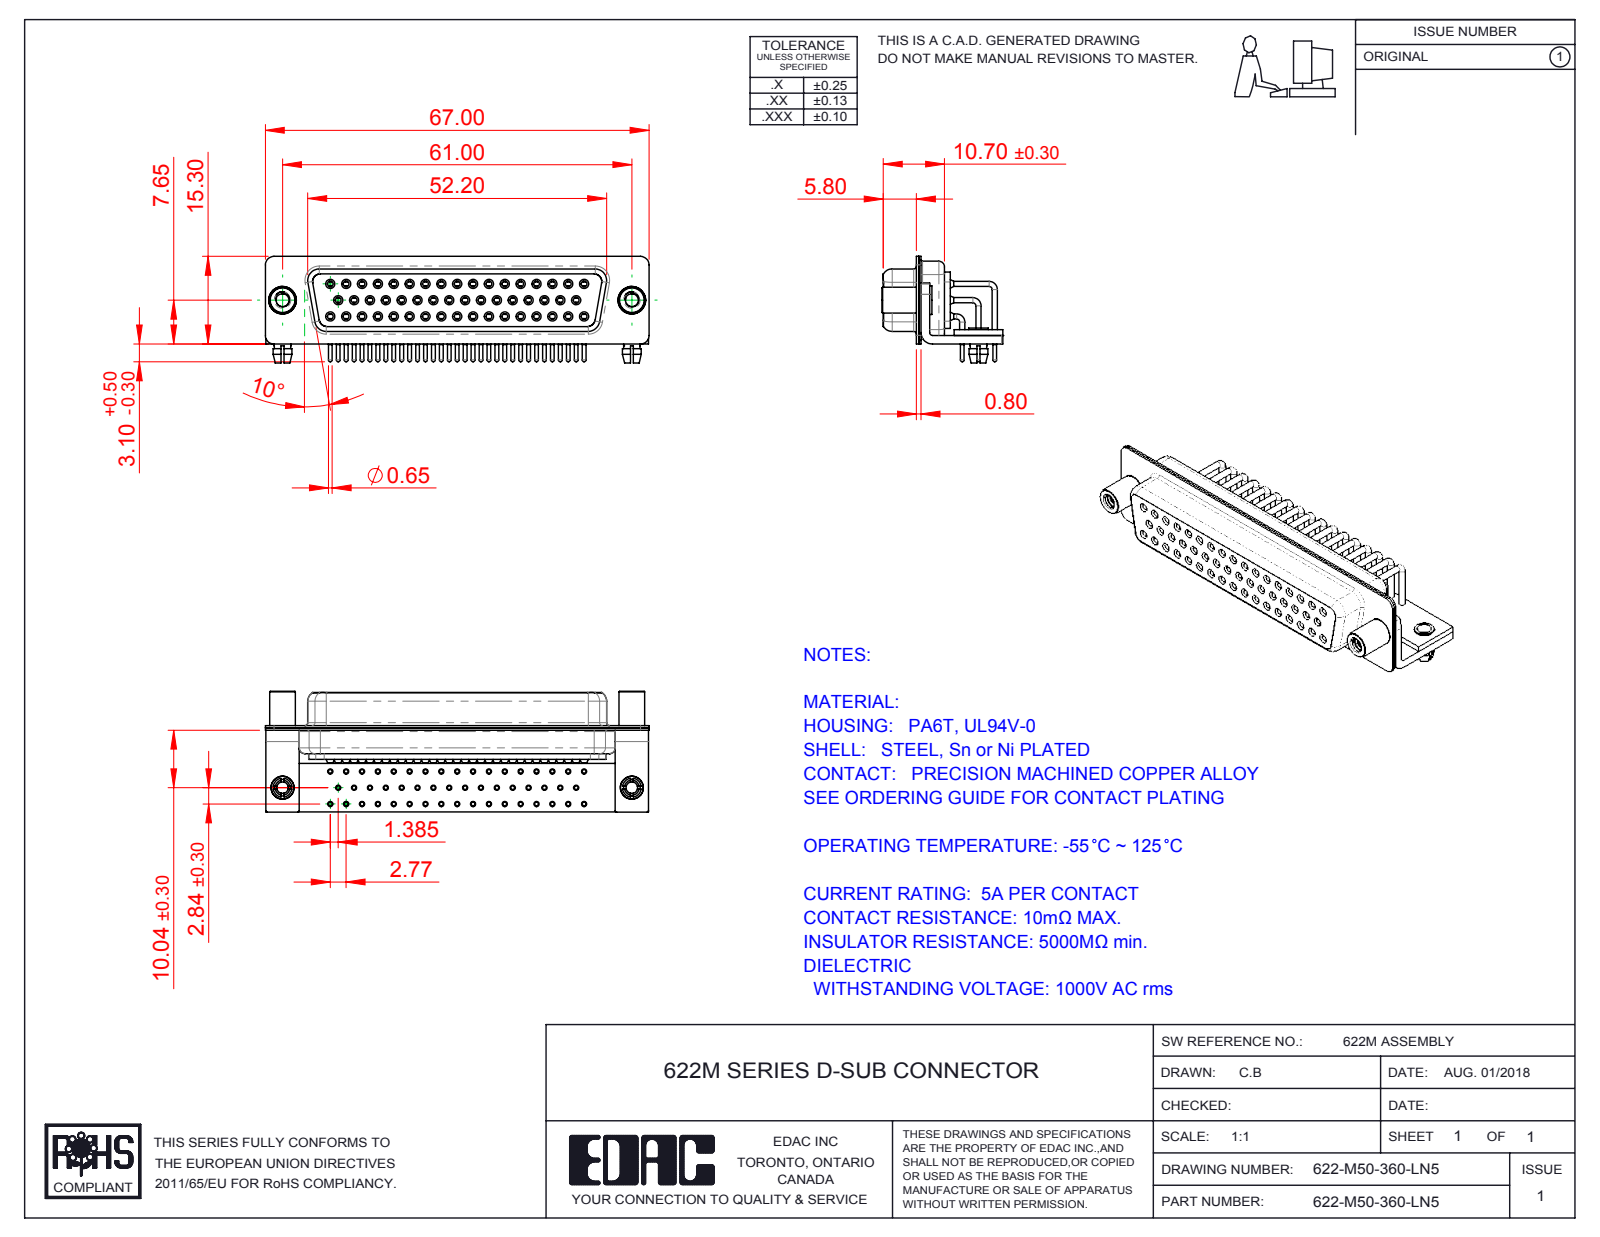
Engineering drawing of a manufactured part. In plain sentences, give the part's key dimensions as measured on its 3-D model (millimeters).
The part is named "622M Housing_50 Contacts; 622-M50-360-LN5; 622M Board Lock_50 Contacts; 622M Stabilizer Board_50 Contacts (+7 more)". Its 3-D file was written by "SolidWorks 2016 (CONFIG_CONTROL_DESIGN)". It is 60 solids with 3221 faces: 893 planar, 1483 cylindrical and 845 other. Overall it measures 67 by 21.1 by 18.6 millimeters. Its volume is 7 917 cubic millimeters and its surface area 18 677 square millimeters. Round holes: 52 of diameter 2, 50 of diameter 0.9, 50 of diameter 1, 50 of diameter 1.1, 50 of diameter 1.7, 50 of diameter 1.8, 2 of diameter 2.26, 2 of diameter 2.5, 2 of diameter 3.2, 2 of diameter 4, 2 of diameter 4.8. Round bosses or shafts: 59 of diameter 0.9, 50 of diameter 1.6, 50 of diameter 1.5, 50 of diameter 0.65, 2 of diameter 5, 2 of diameter 4.9, 2 of diameter 4.5, 2 of diameter 4. Partial cylindrical surfaces (rounded edges, fillets, slot ends): 16 of radius 0.25, 16 of radius 1.5, 13 of radius 2, 8 of radius 1.35, 8 of radius 1.6, 5 of radius 0.5, 4 of radius 0.6, 4 of radius 0.65. The main face-to-face distances are 0.4, 1, 2.2, 0.85, 1.35, 11.85, 12.25, 5.8, 0.8, 5.9. The hole center spacings are 2.77, 3.16, 5.54, 8.31, 11.08, 13.85, 16.62, 19.39.
